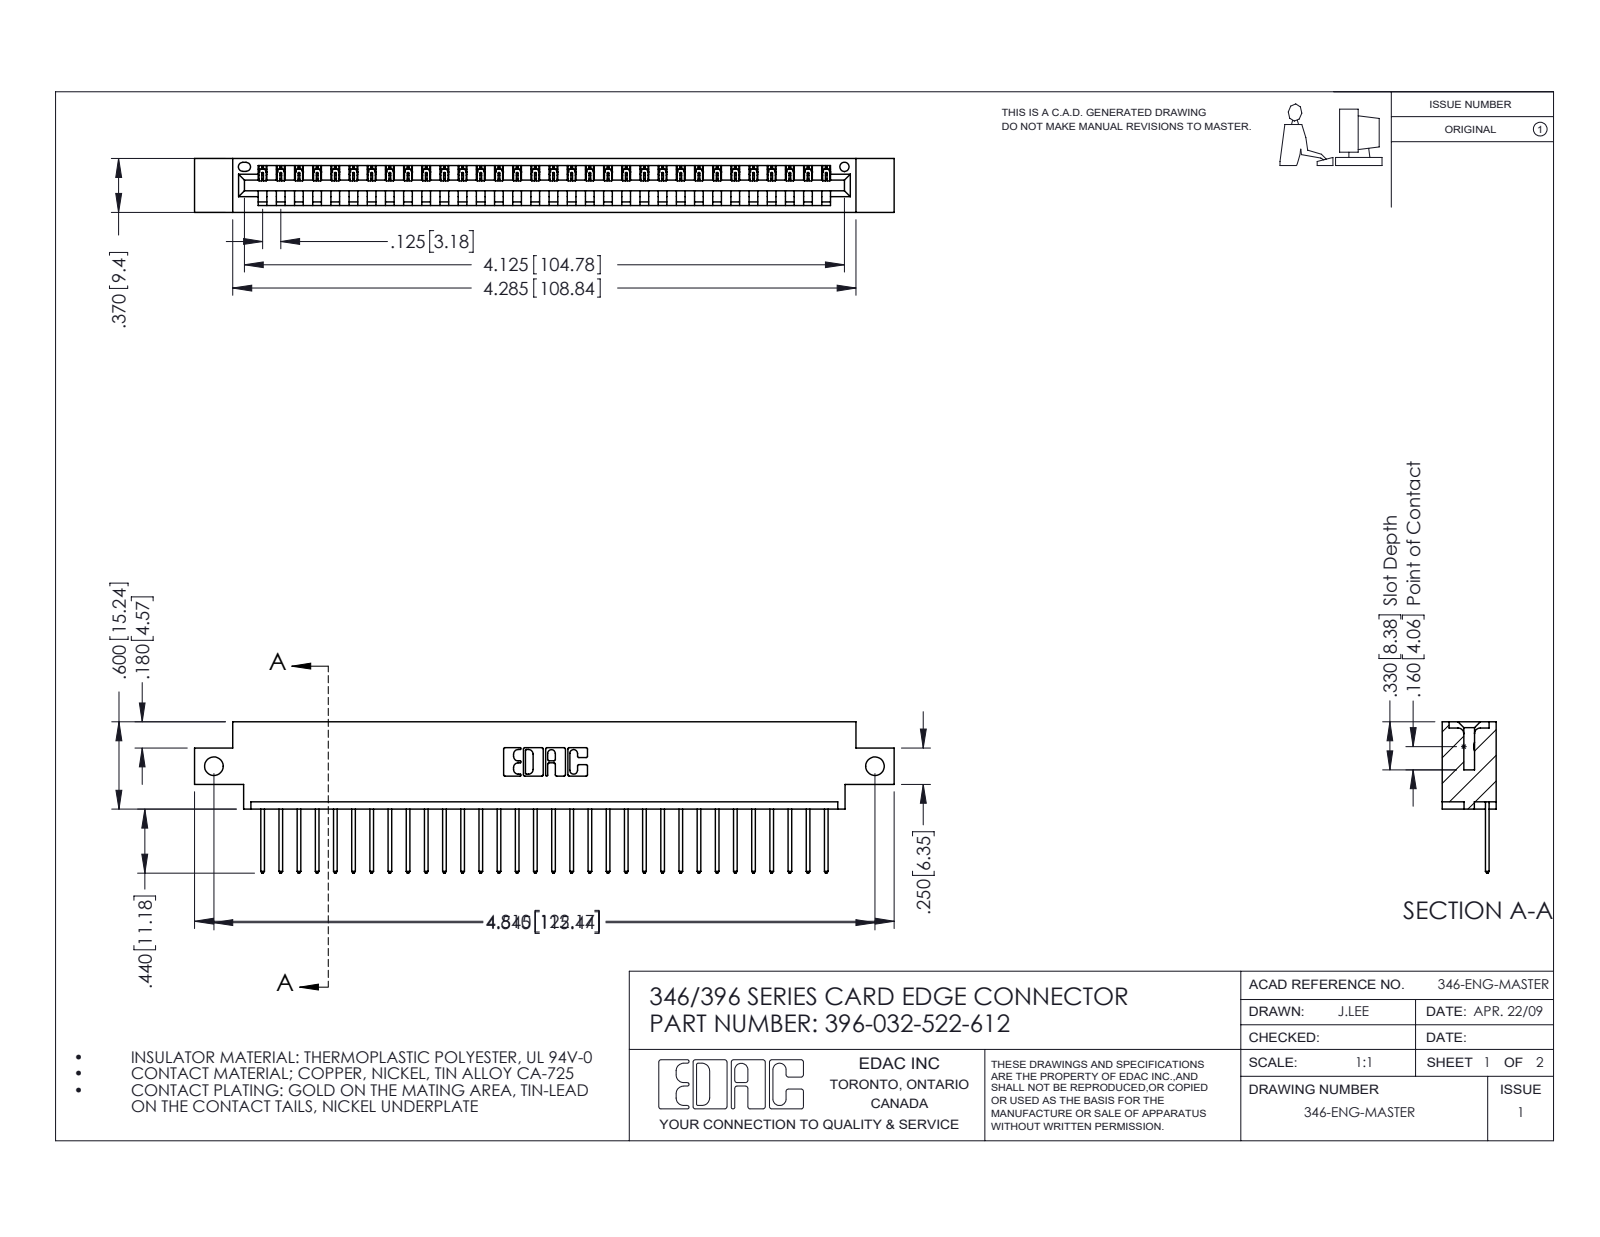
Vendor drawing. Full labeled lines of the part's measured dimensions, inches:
Part name (STEP PRODUCT): 345-292-001_345-293-122; 396-032-522-612; 346 Part_0.170 Offset - Side Mount
STEP written by: SolidWorks 2016 (CONFIG_CONTROL_DESIGN)
Units: inches
Bodies: 33 solids, 1982 faces (1360 planar, 622 cylindrical, 0 other)
Overall size (bounding box): 4.81 × 1.04 × 0.37
Volume: 0.695 in³ · Surface area: 22.1 in²
Round holes (diameter × count): ⌀0.128 ×2, ⌀0.064 ×1
Partial cylindrical surfaces — rounded edges, fillets, slot ends (radius × count): R0.006 ×64, R0.01 ×64, R0.01 ×22, R0.007 ×6, R0.031 ×6, R0.026 ×3, R0.031 ×2, R0.04 ×2
Main face-to-face distances: 0.048, 0.322, 0.37, 0.25, 0.072, 0.298, 0.025, 0.148, 0.222, 0.1
Hole centre spacings: 4.545
